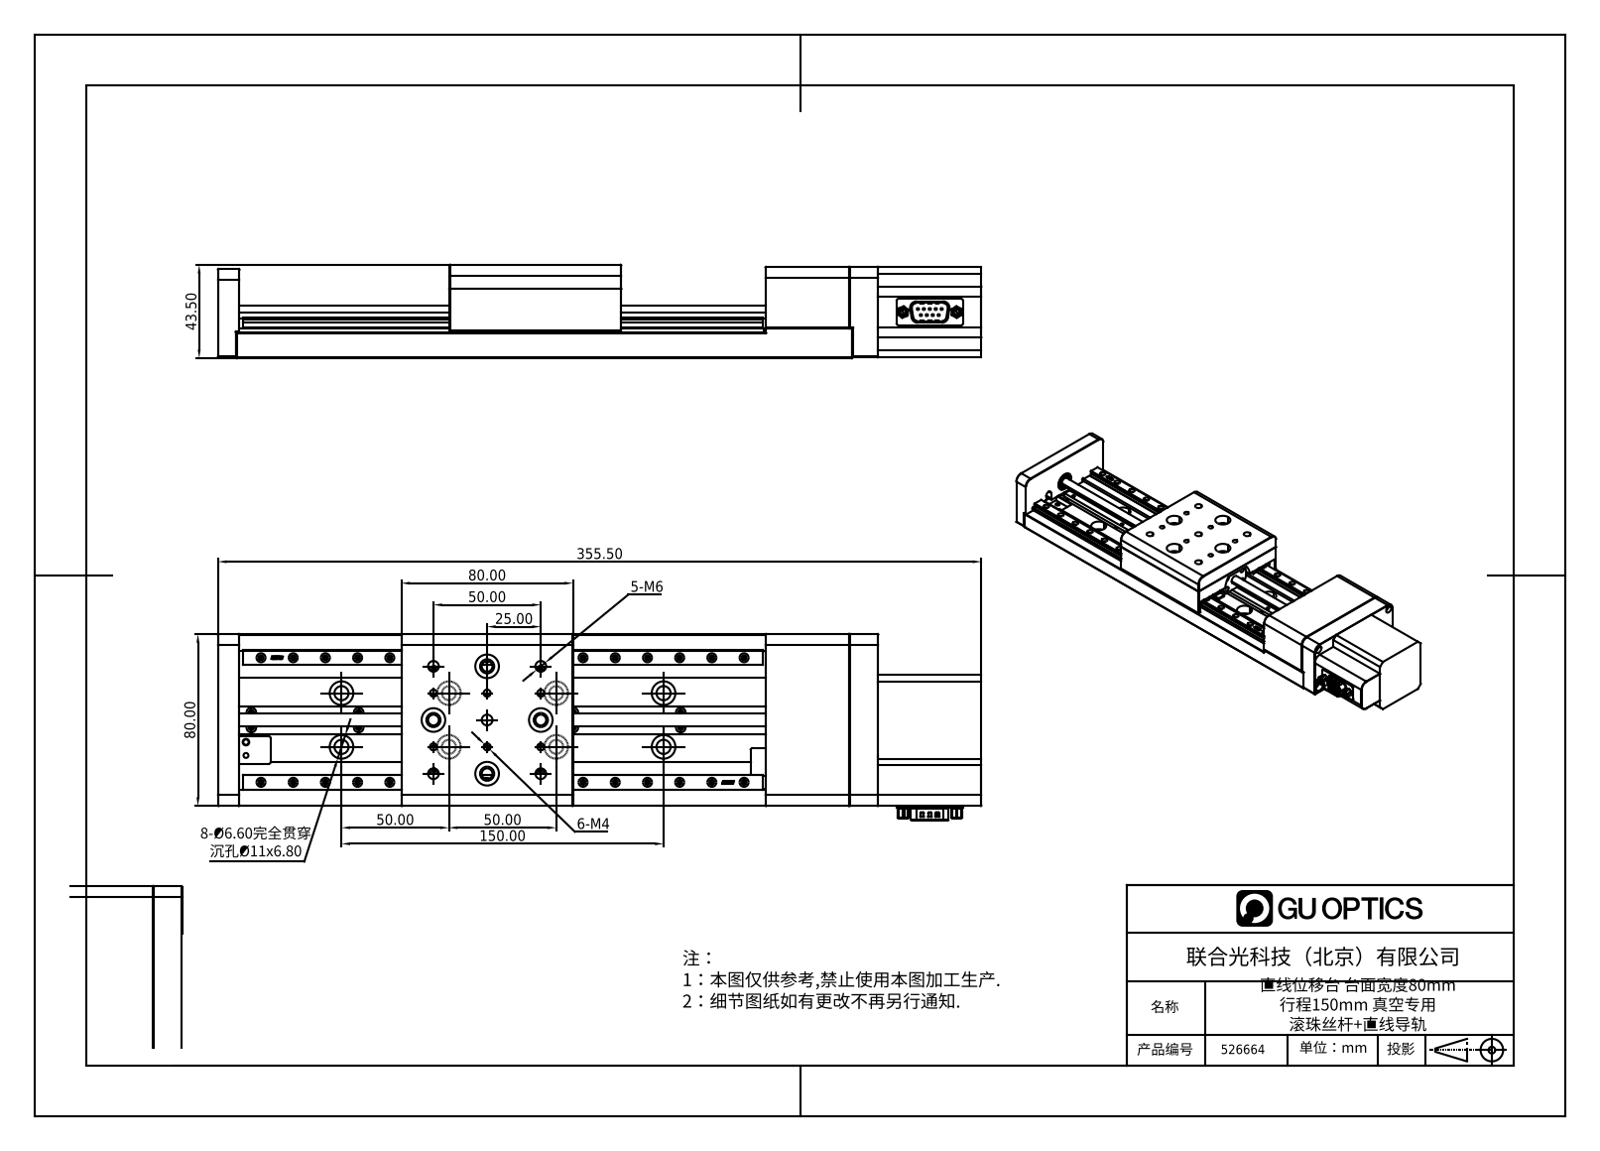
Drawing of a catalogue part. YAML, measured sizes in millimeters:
part_name: "FMS80V-150"
step_written_by: "SolidWorks 2017 (AUTOMOTIVE_DESIGN)"
units: millimeters
bodies: {solids: 25, faces: 2530, planar: 740, cylindrical: 1020, other: 770}
overall_size: [355.5, 86.8, 43.5]
volume: 626616
surface_area: 198844
round_holes:
  - {diameter: 2.4, count: 48}
  - {diameter: 1.6, count: 46}
  - {diameter: 4.2, count: 32}
  - {diameter: 5, count: 25}
  - {diameter: 2.5, count: 22}
  - {diameter: 4.3, count: 16}
  - {diameter: 1.57, count: 12}
  - {diameter: 3.4, count: 12}
  - {diameter: 6.6, count: 12}
  - {diameter: 11, count: 12}
  - {diameter: 1.1, count: 9}
  - {diameter: 3.3, count: 8}
round_bosses_or_shafts:
  - {diameter: 1.5, count: 9}
  - {diameter: 1, count: 9}
  - {diameter: 5, count: 2}
  - {diameter: 3, count: 2}
  - {diameter: 22, count: 1}
  - {diameter: 12, count: 1}
  - {diameter: 7, count: 1}
  - {diameter: 3.8, count: 1}
partial_cylinders:
  - {radius: 0.5, count: 52}
  - {radius: 1, count: 33}
  - {radius: 5, count: 26}
  - {radius: 0.4, count: 10}
  - {radius: 0.3, count: 6}
  - {radius: 2, count: 5}
  - {radius: 0.7, count: 4}
  - {radius: 1.3, count: 4}
face_to_face_distances: [20.5, 0.5, 12, 13.5, 32.5, 10, 32, 2, 11.5, 14]
hole_center_spacings: [50, 100, 50.49, 3.16, 12.04, 17.89, 42.95, 44.94]
